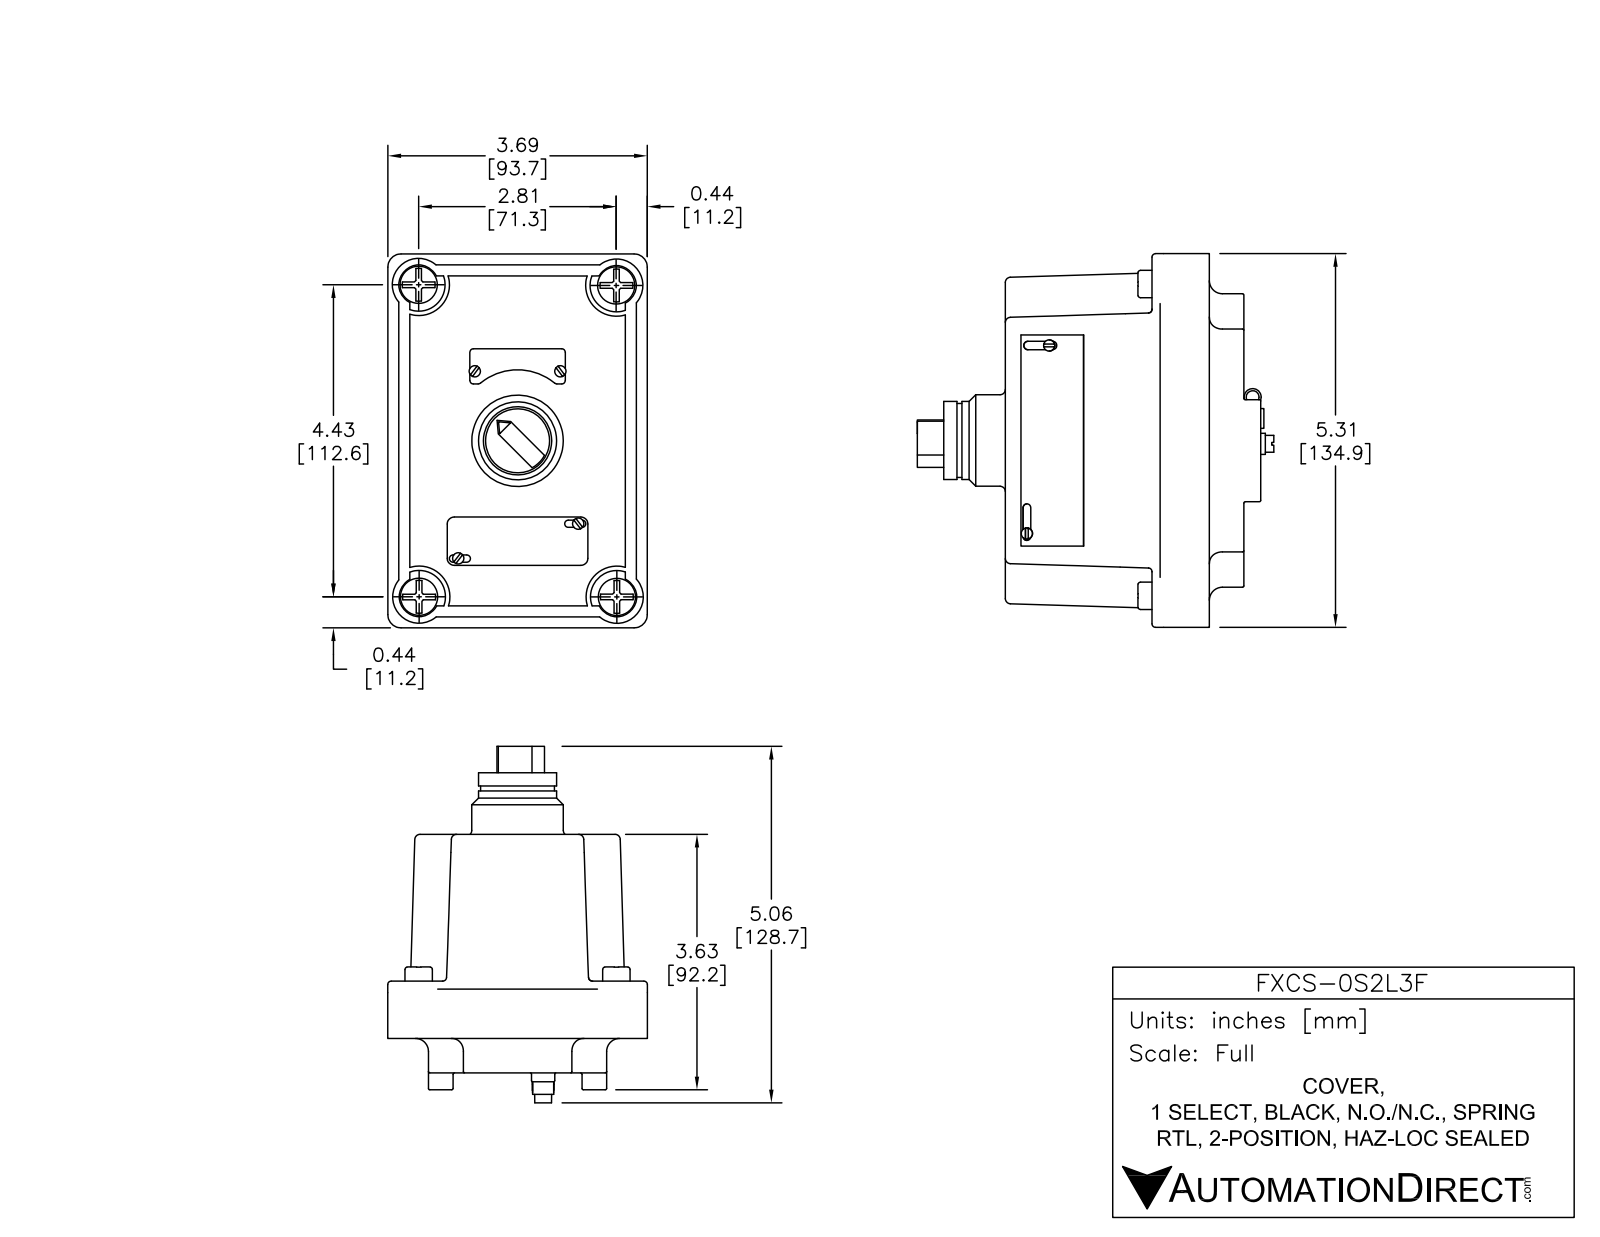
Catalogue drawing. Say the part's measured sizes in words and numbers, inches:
The part is named "FXCS-0S2L3F". Its 3-D file was written by "SolidWorks 2015 (AUTOMOTIVE_DESIGN)". It is 2 solids with 710 faces: 308 planar, 166 cylindrical and 236 other. Overall it measures 5.31 by 5.066 by 3.69 inches. Its volume is 48.91 cubic inches and its surface area 100.9 square inches. Round holes: 8 of diameter 0.16, 1 of diameter 0.198, 1 of diameter 0.97. Round bosses or shafts: 8 of diameter 0.16, 4 of diameter 0.39, 1 of diameter 1.3, 1 of diameter 1.11, 1 of diameter 1.05, 1 of diameter 0.91, 1 of diameter 0.33, 1 of diameter 0.3. Partial cylindrical surfaces (rounded edges, fillets, slot ends): 24 of radius 0.05, 22 of radius 0.02, 4 of radius 0.051, 4 of radius 0.055, 4 of radius 0.06, 4 of radius 0.075, 4 of radius 0.1, 4 of radius 0.185. The main face-to-face distances are 3.39, 0.49, 2.9, 0.021, 3.69, 0.578, 3.111, 1.19, 0.7, 2.2. The hole center spacings are 0.25, 2.197, 0.5, 2.183, 2.239, 0.75, 1.092, 1.115.
